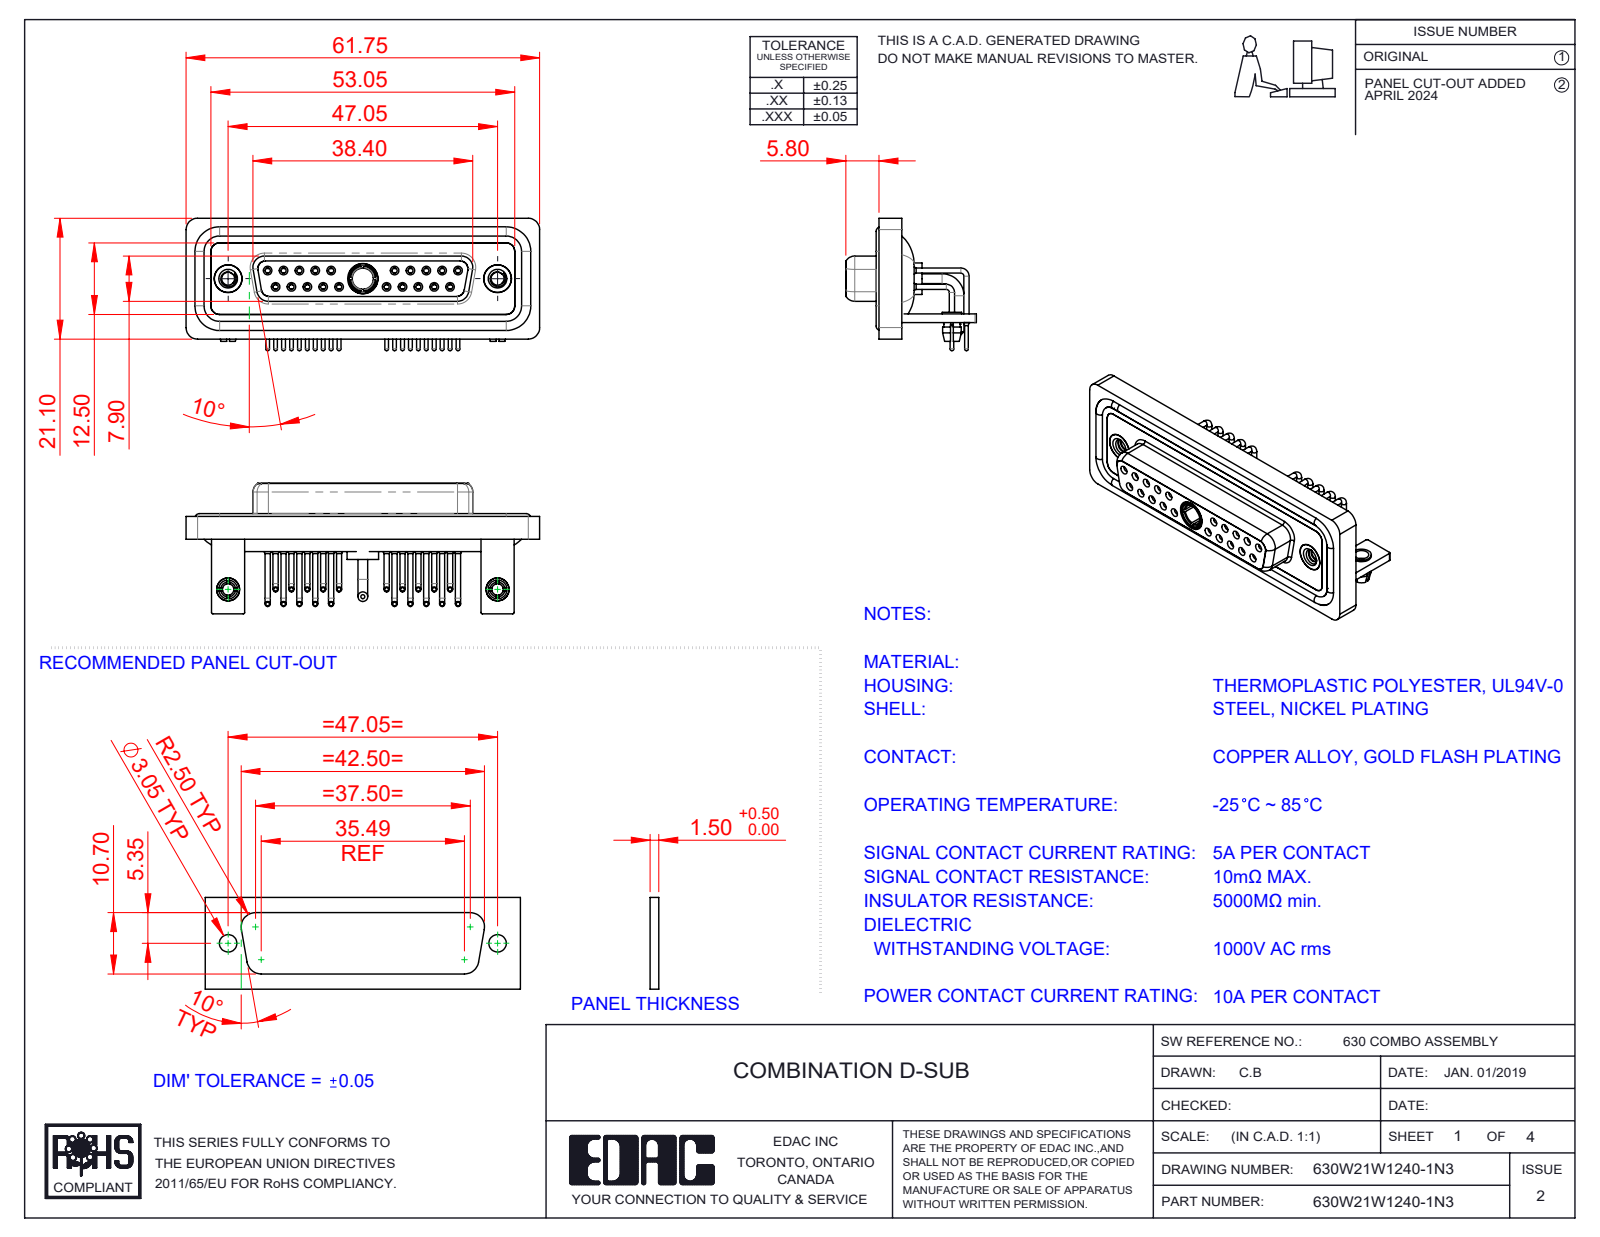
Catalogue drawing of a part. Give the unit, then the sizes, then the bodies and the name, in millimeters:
Units: millimetres
Overall size (bounding box): 61.75 × 23.12 × 22.8
Round holes (diameter × count): ⌀2 ×22, ⌀0.9 ×20, ⌀1.1 ×20, ⌀1.5 ×20, ⌀1.6 ×10, ⌀1.7 ×10, ⌀4.85 ×3, ⌀2.26 ×2, ⌀2.5 ×2, ⌀3.2 ×2, ⌀4 ×2, ⌀4.05 ×2
Round bosses / shafts (diameter × count): ⌀0.9 ×20, ⌀0.65 ×20, ⌀1.6 ×14, ⌀4.95 ×2, ⌀4.8 ×2, ⌀4 ×2, ⌀3.4 ×2, ⌀3.3 ×2
Partial cylindrical surfaces — rounded edges, fillets, slot ends (radius × count): R2 ×19, R1.5 ×18, R0.25 ×16, R1.35 ×8, R1.6 ×8, R0.5 ×5, R0.6 ×4, R0.65 ×4
Main face-to-face distances: 0.4, 1.8, 2.9, 3.7, 1.5, 4.1, 1.1, 1.4, 1.6, 2.5
Hole centre spacings: 3.16, 2.77, 5.54, 8.31, 5.04, 19.39, 20.97, 22.16
Volume: 8 851 mm³ · Surface area: 15 675 mm²
Bodies: 33 solids, 1664 faces (502 planar, 729 cylindrical, 433 other)
Part name (STEP PRODUCT): 630Combo Housing_21W1; 630Combo Shell Rear_25 Contacts; 630Combo Waterproof Housing_25 Contacts; 630Combo Contact Row 1_50 Contacts (+7 more)
STEP written by: SolidWorks 2023 (CONFIG_CONTROL_DESIGN)
